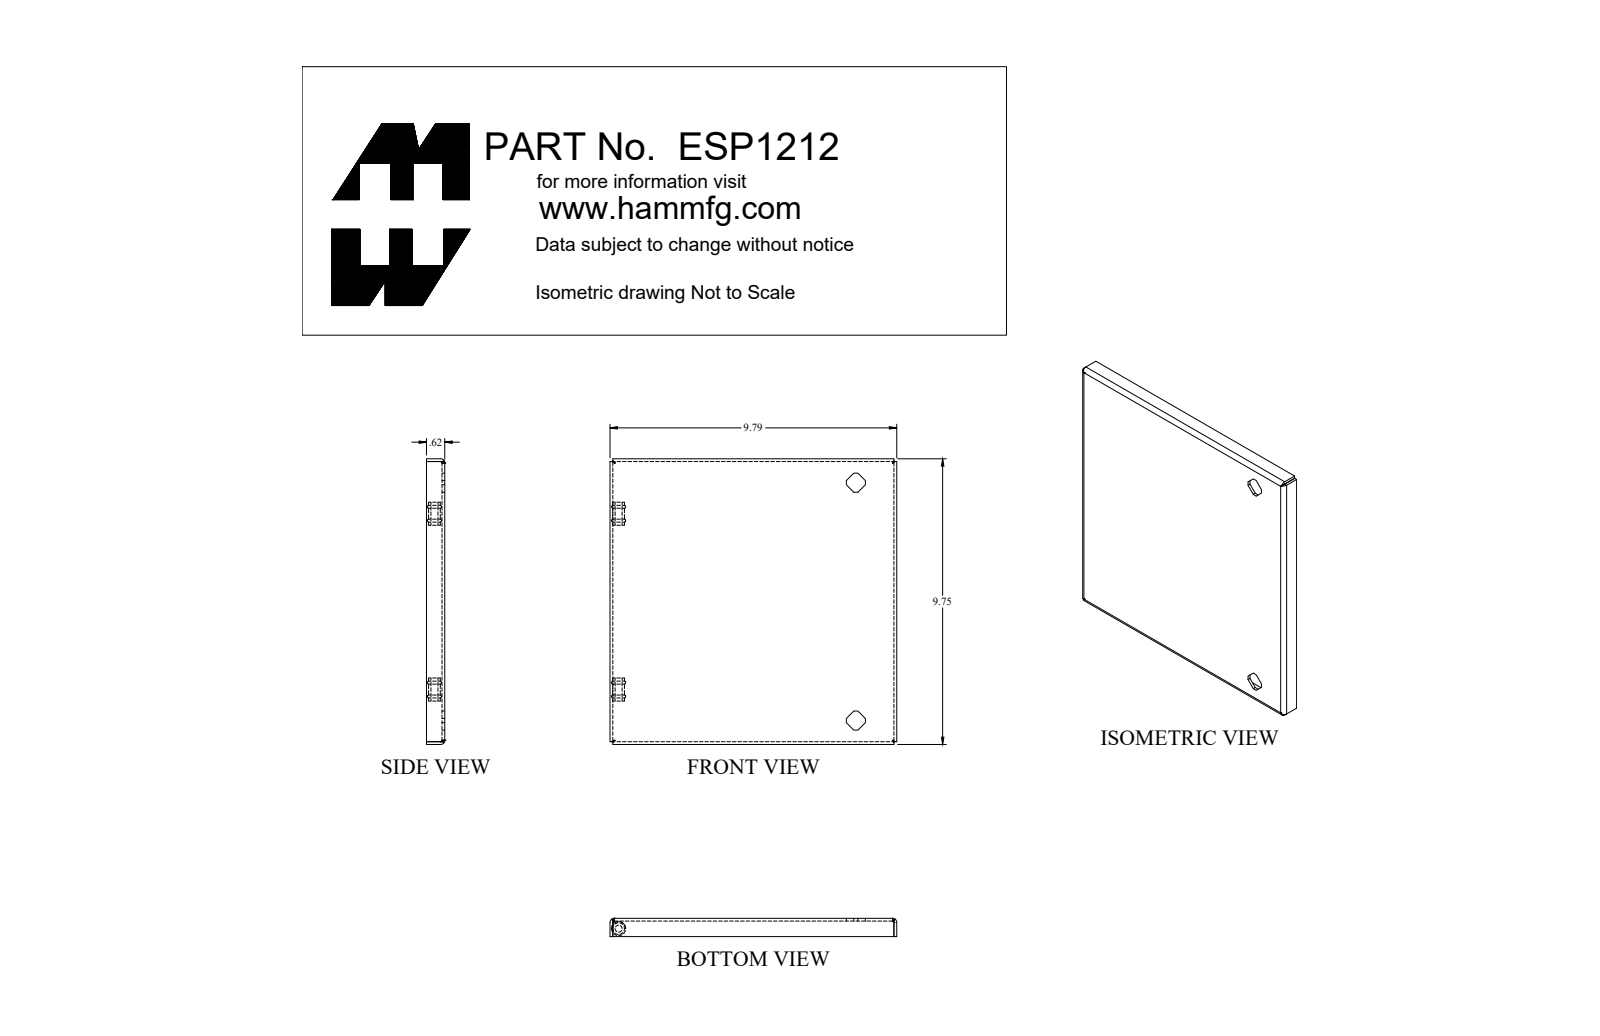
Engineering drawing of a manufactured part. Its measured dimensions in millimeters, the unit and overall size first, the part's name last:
Units: millimetres
Overall size (bounding box): 297.3 × 252.8 × 247.7
Round holes (diameter × count): ⌀3.5 ×2, ⌀6.1 ×2, ⌀13.1 ×2
Round bosses / shafts (diameter × count): ⌀5.9 ×6, ⌀20 ×2, ⌀13.6 ×2, ⌀12.6 ×2, ⌀11 ×2, ⌀9 ×2
Partial cylindrical surfaces — rounded edges, fillets, slot ends (radius × count): R1.2 ×28, R0.3 ×24, R0.9 ×6, R2.7 ×6, R1.5 ×4, R3.6 ×4, R3.9 ×4, R4 ×4
Main face-to-face distances: 2.4, 1, 1.8, 20.7, 19.7, 19.7, 204.8, 276.7, 1, 18.7
Hole centre spacings: 152.4, 207.2
Volume: 328 700 mm³ · Surface area: 380 800 mm²
Bodies: 13 solids, 584 faces (354 planar, 174 cylindrical, 56 other)
Part name (STEP PRODUCT): ESP1212
STEP written by: SolidWorks 2018 (AUTOMOTIVE_DESIGN)
